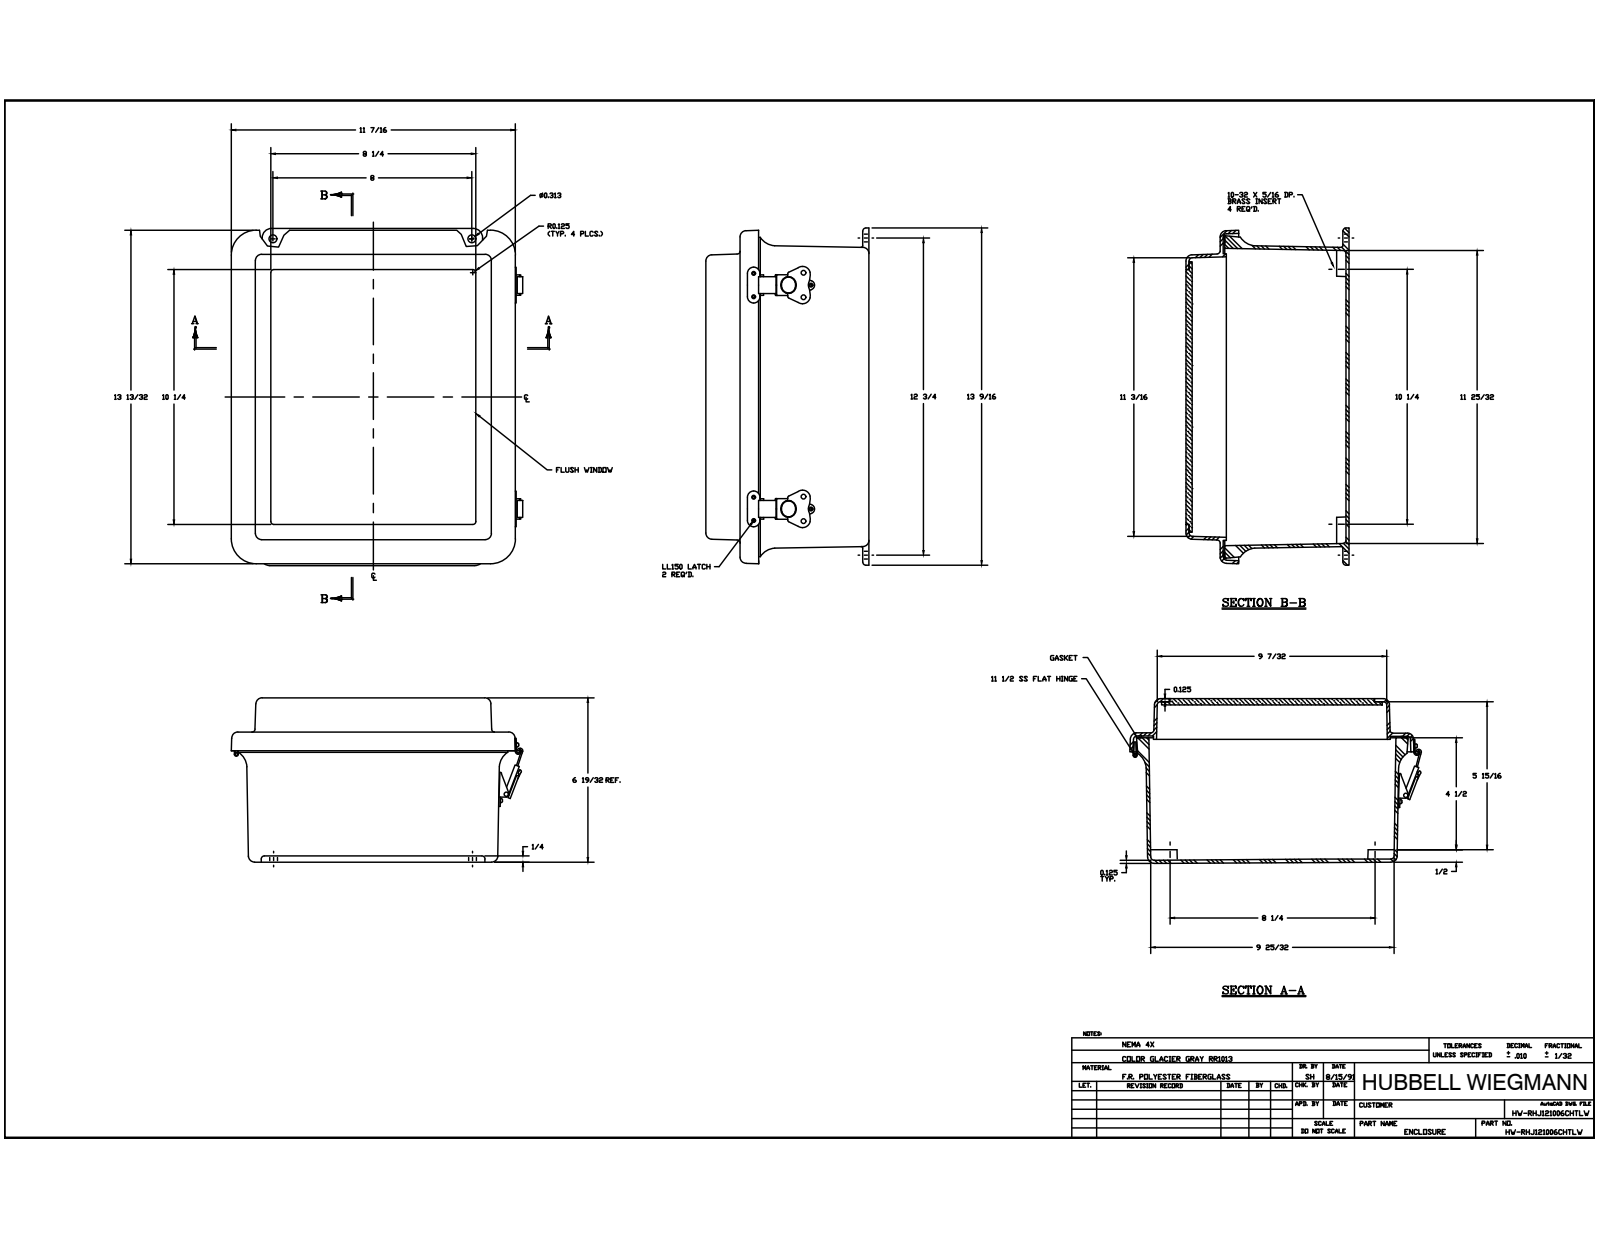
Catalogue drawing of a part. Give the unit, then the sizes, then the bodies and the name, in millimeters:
Units: millimetres
Overall size (bounding box): 344.49 × 294.9 × 167.33
Round holes (diameter × count): ⌀3.56 ×16, ⌀3.33 ×8, ⌀3.86 ×5, ⌀3.3 ×4, ⌀3.96 ×4, ⌀4.2 ×4, ⌀5 ×4, ⌀5.54 ×4, ⌀3 ×2, ⌀3.5 ×2, ⌀4.61 ×2, ⌀4.62 ×2
Round bosses / shafts (diameter × count): ⌀6.35 ×16, ⌀3.17 ×16, ⌀6.86 ×4, ⌀14.8 ×2, ⌀13.3 ×2, ⌀5.3 ×2, ⌀4.7 ×2, ⌀3.25 ×2
Partial cylindrical surfaces — rounded edges, fillets, slot ends (radius × count): R3.17 ×24, R0.79 ×20, R6.35 ×20, R2 ×19, R0.95 ×8, R1 ×8, R1.15 ×8, R1.2 ×8
Main face-to-face distances: 3.18, 164.15, 6.35, 160.98, 157.8, 167.33, 128.92, 35.23, 125.74, 32.06
Hole centre spacings: 228.6, 92.08, 17.79, 23.82, 34.24, 37.21, 55.59, 229.39
Volume: 1 708 000 mm³ · Surface area: 867 168 mm²
Bodies: 49 solids, 1239 faces (551 planar, 473 cylindrical, 215 other)
Part name (STEP PRODUCT): J1210HL_9; RMINS45821P_219; RMINS45821P_220; RMINS45821P_221 (+8 more)
STEP written by: Autodesk Inventor 2014 (AUTOMOTIVE_DESIGN)
